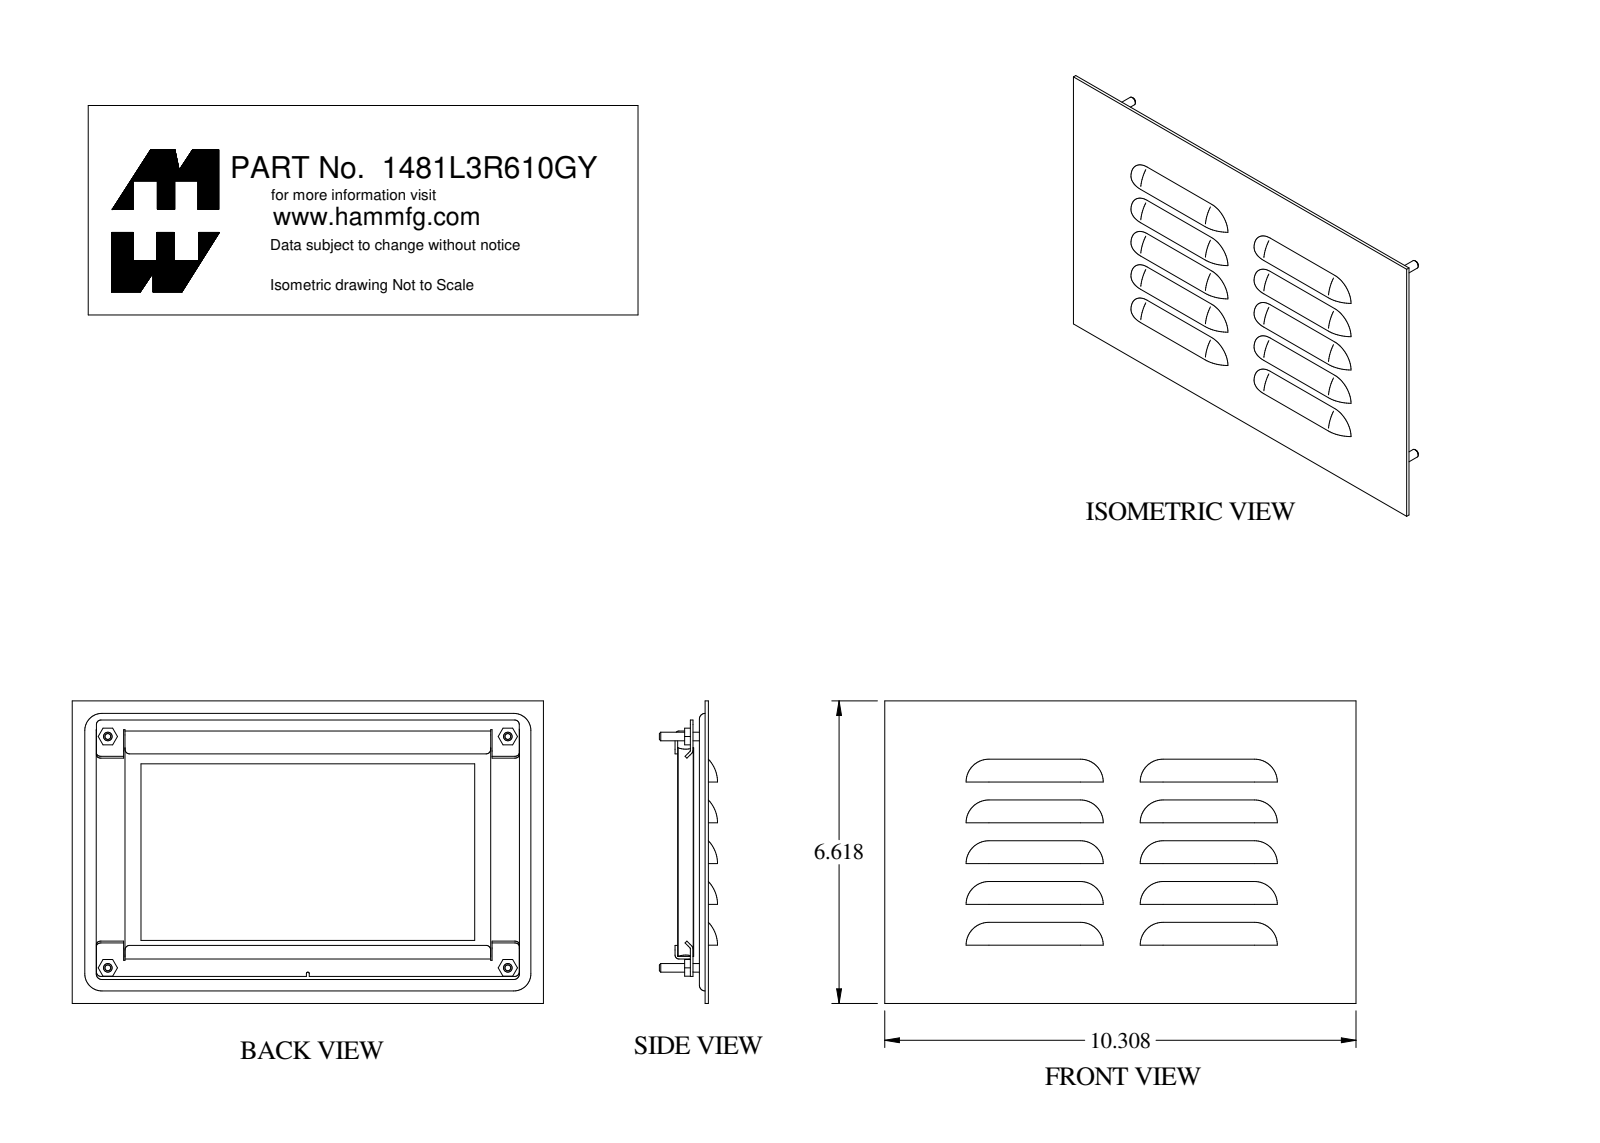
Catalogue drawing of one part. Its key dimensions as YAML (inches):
part_name: "1481L3R610GY"
step_written_by: "SolidWorks 2021 (AUTOMOTIVE_DESIGN)"
units: inches
bodies: {solids: 13, faces: 313, planar: 155, cylindrical: 98, other: 60}
overall_size: [10.308, 6.618, 1.272]
volume: 16.7
surface_area: 307.7
round_holes:
  - {diameter: 0.156, count: 4}
  - {diameter: 0.22, count: 4}
round_bosses_or_shafts:
  - {diameter: 0.25, count: 4}
  - {diameter: 0.188, count: 4}
partial_cylinders:
  - {radius: 0.1, count: 12}
  - {radius: 0.029, count: 6}
  - {radius: 0.086, count: 6}
  - {radius: 0.653, count: 5}
  - {radius: 0.725, count: 5}
  - {radius: 0.125, count: 4}
  - {radius: 0.126, count: 4}
  - {radius: 0.374, count: 4}
face_to_face_distances: [0.072, 0.3, 0.25, 0.372, 0.622, 0.55, 0.05, 0.057, 0.322, 0.6]
hole_center_spacings: [5.06, 10.107, 8.75, 8.75]
